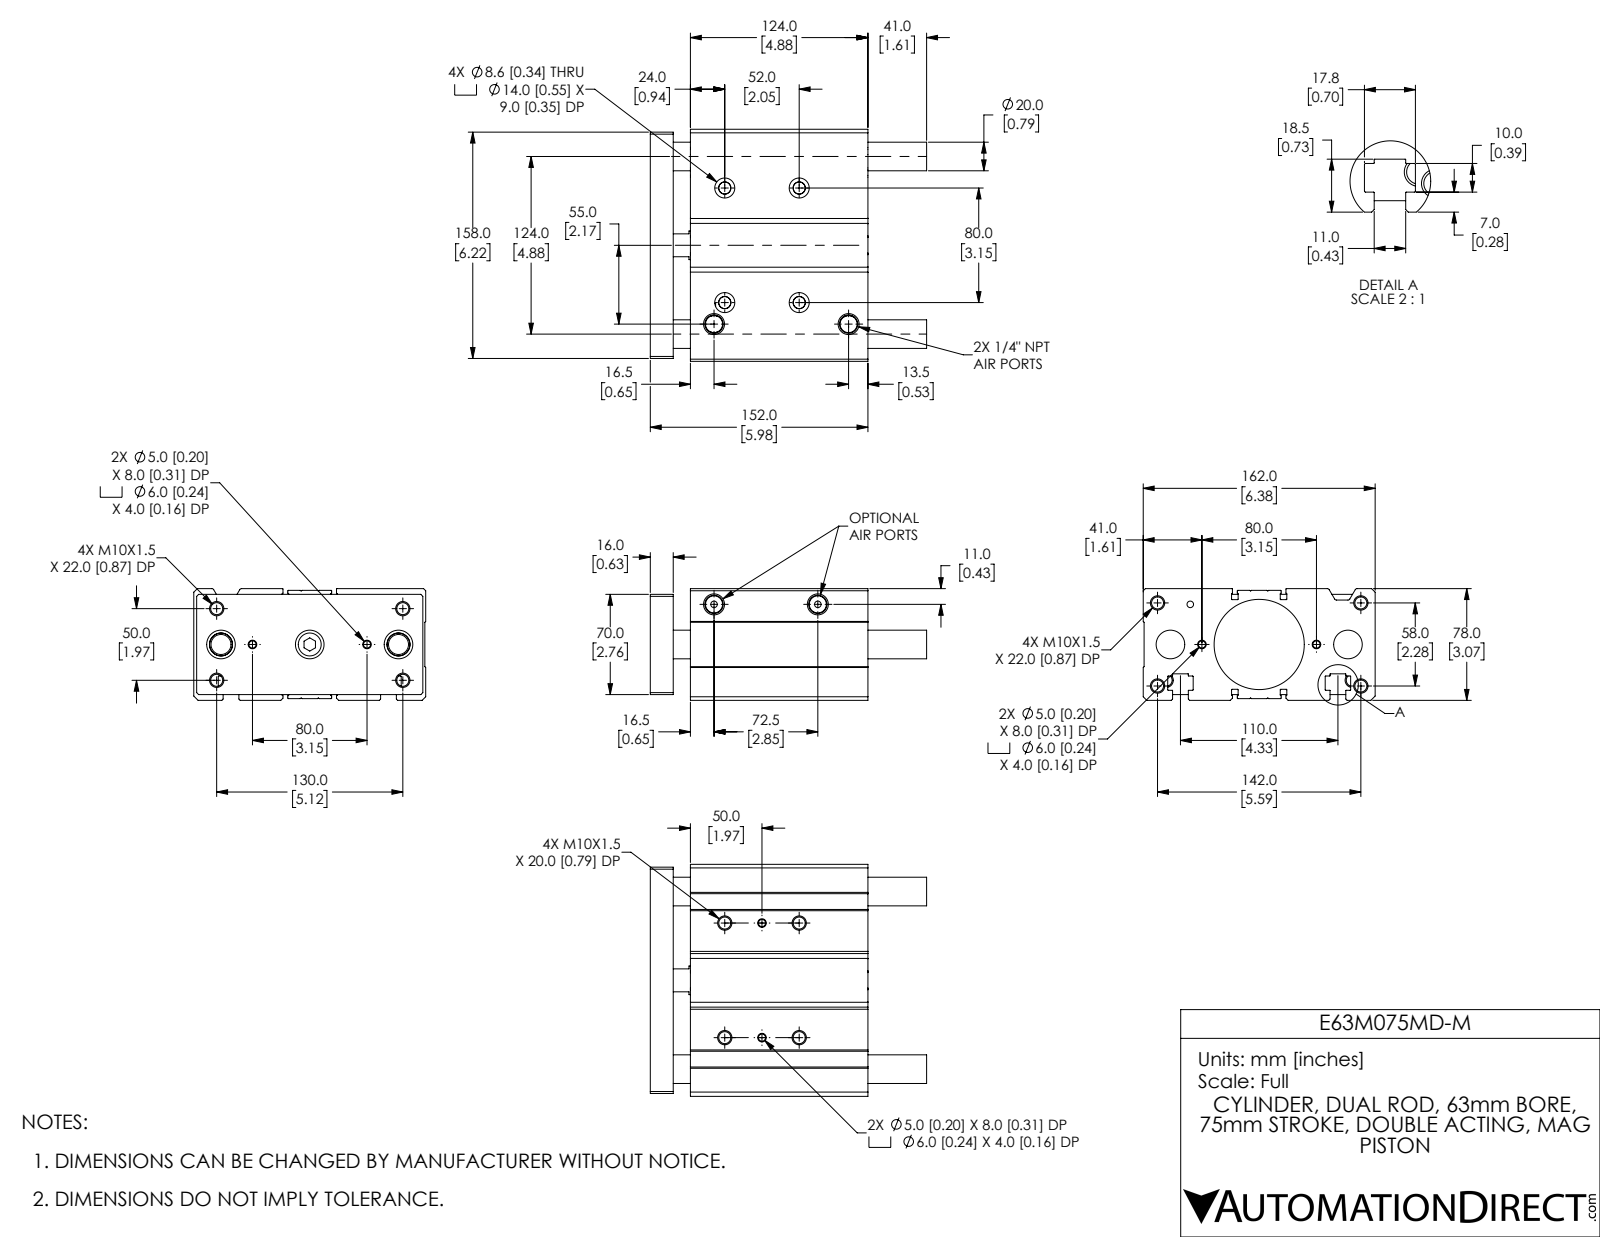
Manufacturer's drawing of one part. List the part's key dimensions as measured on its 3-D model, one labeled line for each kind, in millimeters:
Part name (STEP PRODUCT): E63M075MD-M_BODY; E63M075MD-M_ENDPLATE; E63M075MD-M
STEP written by: SolidWorks 2019 (CONFIG_CONTROL_DESIGN)
Units: millimetres
Bodies: 5 solids, 421 faces (139 planar, 190 cylindrical, 92 other)
Overall size (bounding box): 193 × 162 × 78
Volume: 1 413 000 mm³ · Surface area: 238 075 mm²
Round holes (diameter × count): ⌀8.38 ×12, ⌀5 ×4, ⌀6 ×4, ⌀8.6 ×4, ⌀14 ×4, ⌀4.57 ×3, ⌀10 ×3, ⌀20 ×3, ⌀16 ×2, ⌀20 ×1, ⌀63 ×1, ⌀63 ×1
Round bosses / shafts (diameter × count): ⌀16 ×1
Partial cylindrical surfaces — rounded edges, fillets, slot ends (radius × count): R0.2 ×32, R0.4 ×28, R1.5 ×4, R0.3 ×2
Main face-to-face distances: 78, 28, 16, 12, 152, 136, 124, 4, 1.2, 76.8
Hole centre spacings: 7.21, 25.18, 26, 30.36, 35.36, 42.45, 54.33, 69.64
